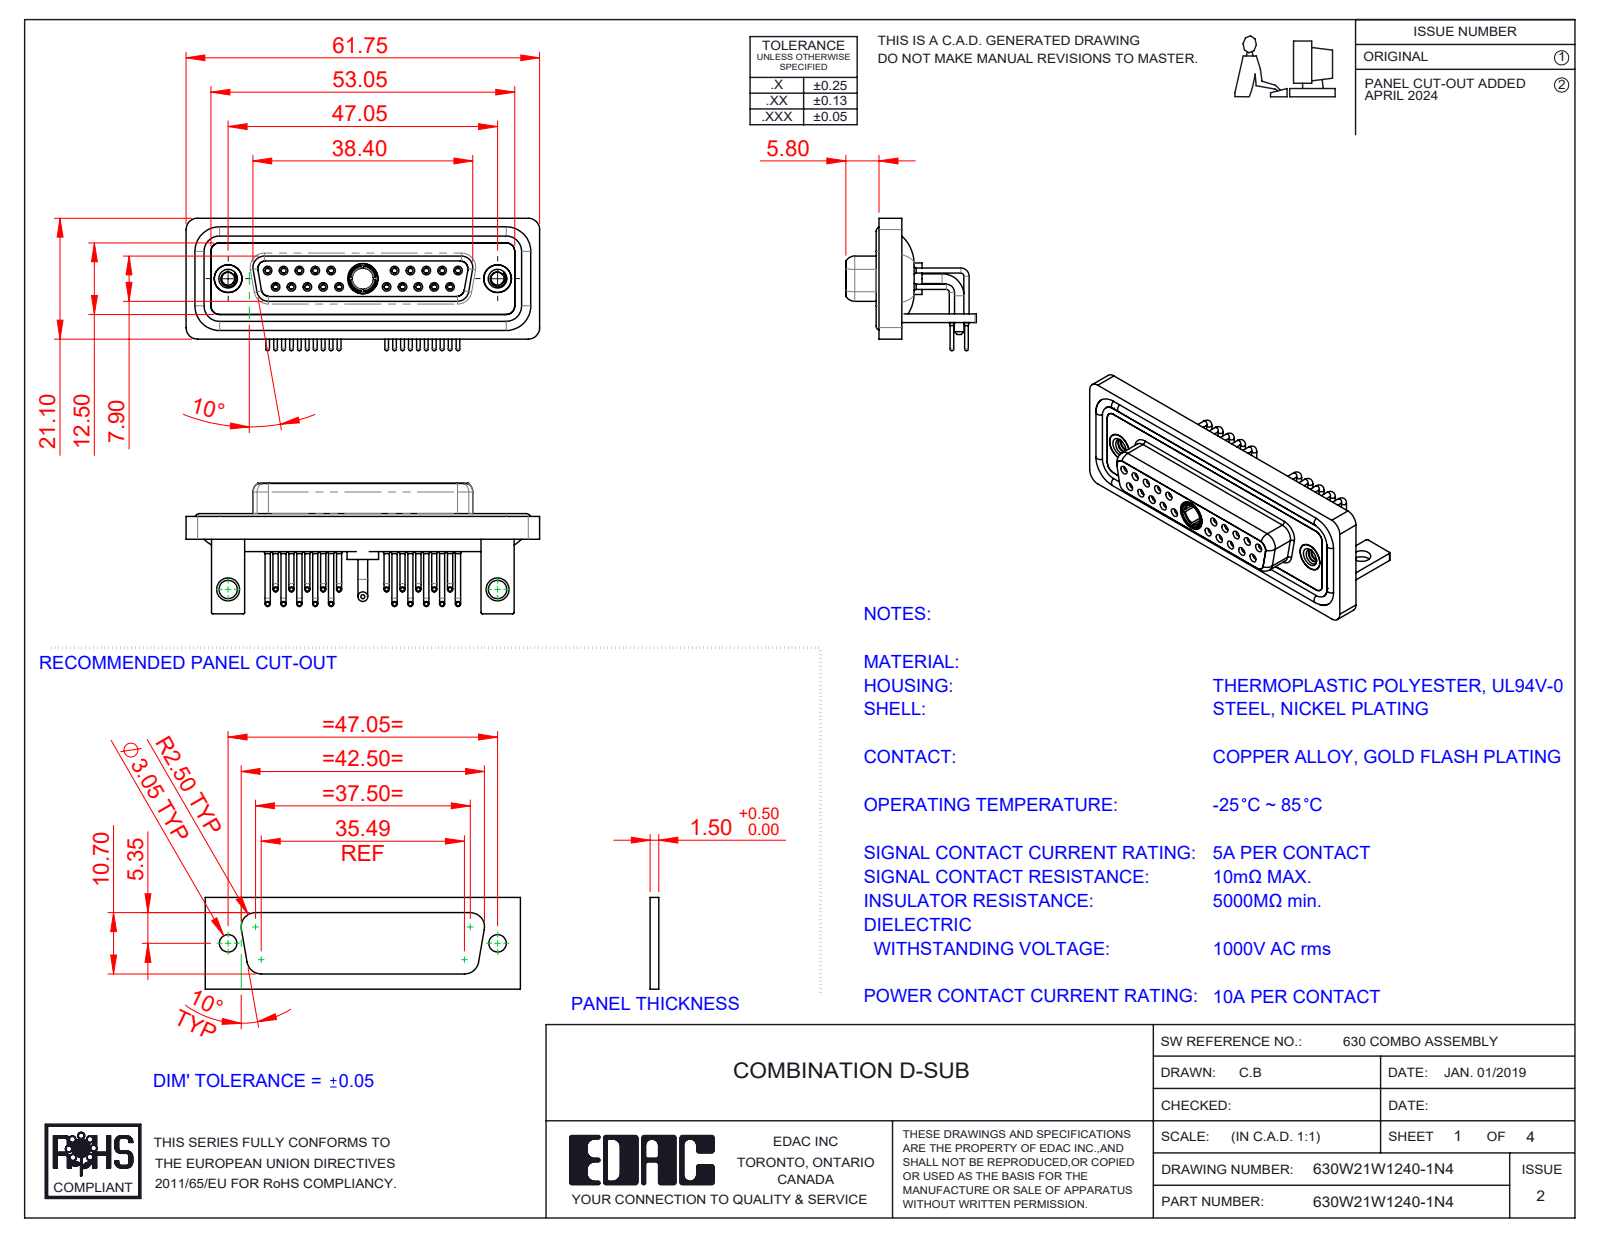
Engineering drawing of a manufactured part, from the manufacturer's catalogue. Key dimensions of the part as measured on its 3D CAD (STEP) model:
Part name (STEP PRODUCT): 630Combo Shell Rear_25 Contacts; 630Combo Threaded Rivet_2; 630Combo Housing_21W1; 630Combo Shell Front_25 Contacts (+6 more)
STEP written by: SolidWorks 2023 (CONFIG_CONTROL_DESIGN)
Units: millimetres
Bodies: 31 solids, 1572 faces (454 planar, 697 cylindrical, 421 other)
Overall size (bounding box): 61.75 × 23.12 × 22.8
Volume: 8 814 mm³ · Surface area: 15 464 mm²
Round holes (diameter × count): ⌀0.9 ×20, ⌀1.1 ×20, ⌀1.5 ×20, ⌀2 ×20, ⌀1.6 ×10, ⌀1.7 ×10, ⌀4.85 ×3, ⌀2.26 ×2, ⌀3.2 ×2, ⌀4 ×2, ⌀4.05 ×2, ⌀5 ×2
Round bosses / shafts (diameter × count): ⌀0.9 ×20, ⌀0.65 ×20, ⌀1.6 ×14, ⌀4.95 ×2, ⌀4.8 ×2, ⌀1.7 ×2, ⌀5.5 ×1, ⌀5.2 ×1
Partial cylindrical surfaces — rounded edges, fillets, slot ends (radius × count): R2 ×19, R1.5 ×18, R0.25 ×16, R1.35 ×8, R1.6 ×8, R0.5 ×5, R0.6 ×4, R0.65 ×4
Main face-to-face distances: 0.4, 1.8, 2.9, 3.7, 1.5, 4.1, 1.1, 1.4, 1.6, 2.5
Hole centre spacings: 3.16, 2.77, 5.54, 8.31, 5.04, 19.39, 20.97, 22.16
